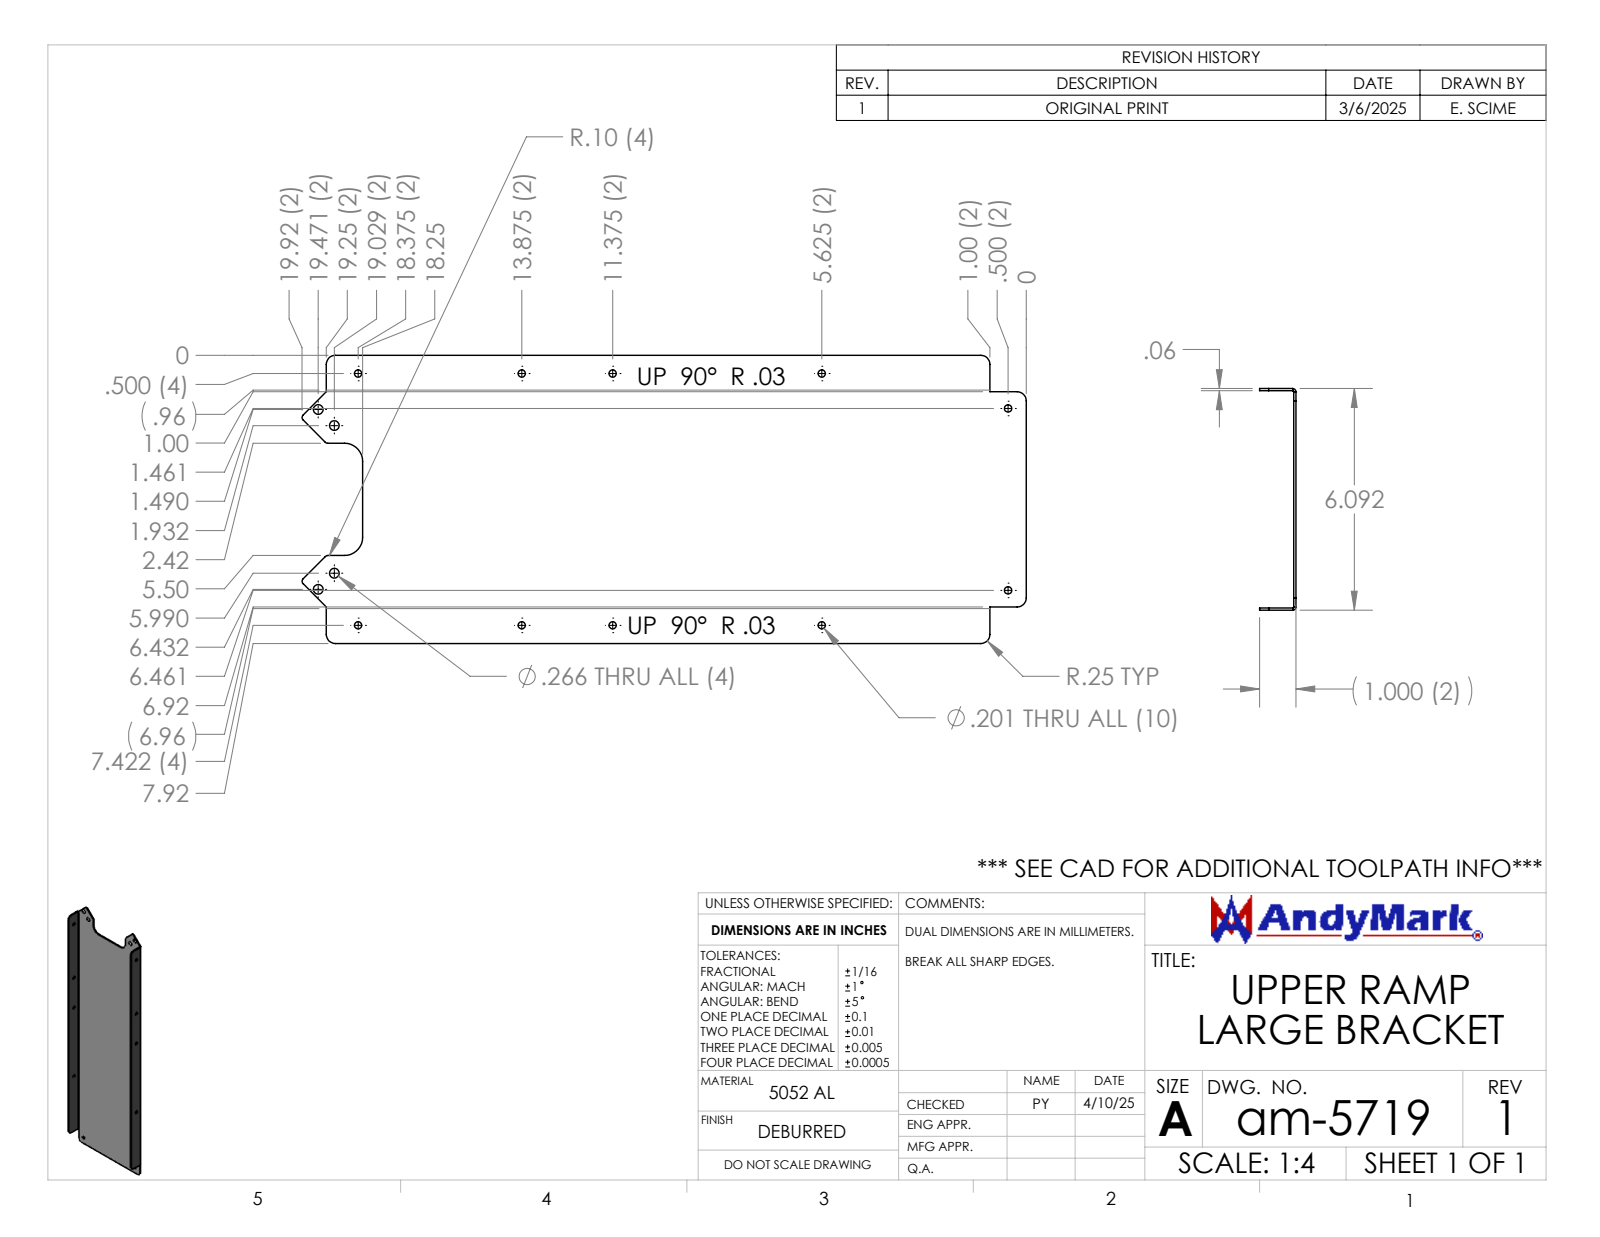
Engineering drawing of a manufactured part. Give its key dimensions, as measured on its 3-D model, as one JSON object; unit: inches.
{"part_name": "am-5719 Upper Ramp Larger Bracket", "step_written_by": "SolidWorks 2024 (AUTOMOTIVE_DESIGN)", "units": "inches", "bodies": {"solids": 1, "faces": 70, "planar": 26, "cylindrical": 44, "other": 0}, "overall_size": [19.916, 6.092, 1], "volume_in3": 8.873, "surface_area_in2": 299.7, "round_holes": [[0.201, 6], [0.266, 4]], "partial_cylinders_radius": [[0.1, 4], [0.25, 4], [0.029, 2], [0.089, 2], [0.5, 2]], "face_to_face_distances": [0.06, 0.06, 6.032, 6.092, 5.972, 6.032, 1, 0.94, 18.25, 3.181], "hole_center_spacings": [0.625, 4.522, 18.535, 18.971, 19.611, 2.5, 4.058, 4.5]}
